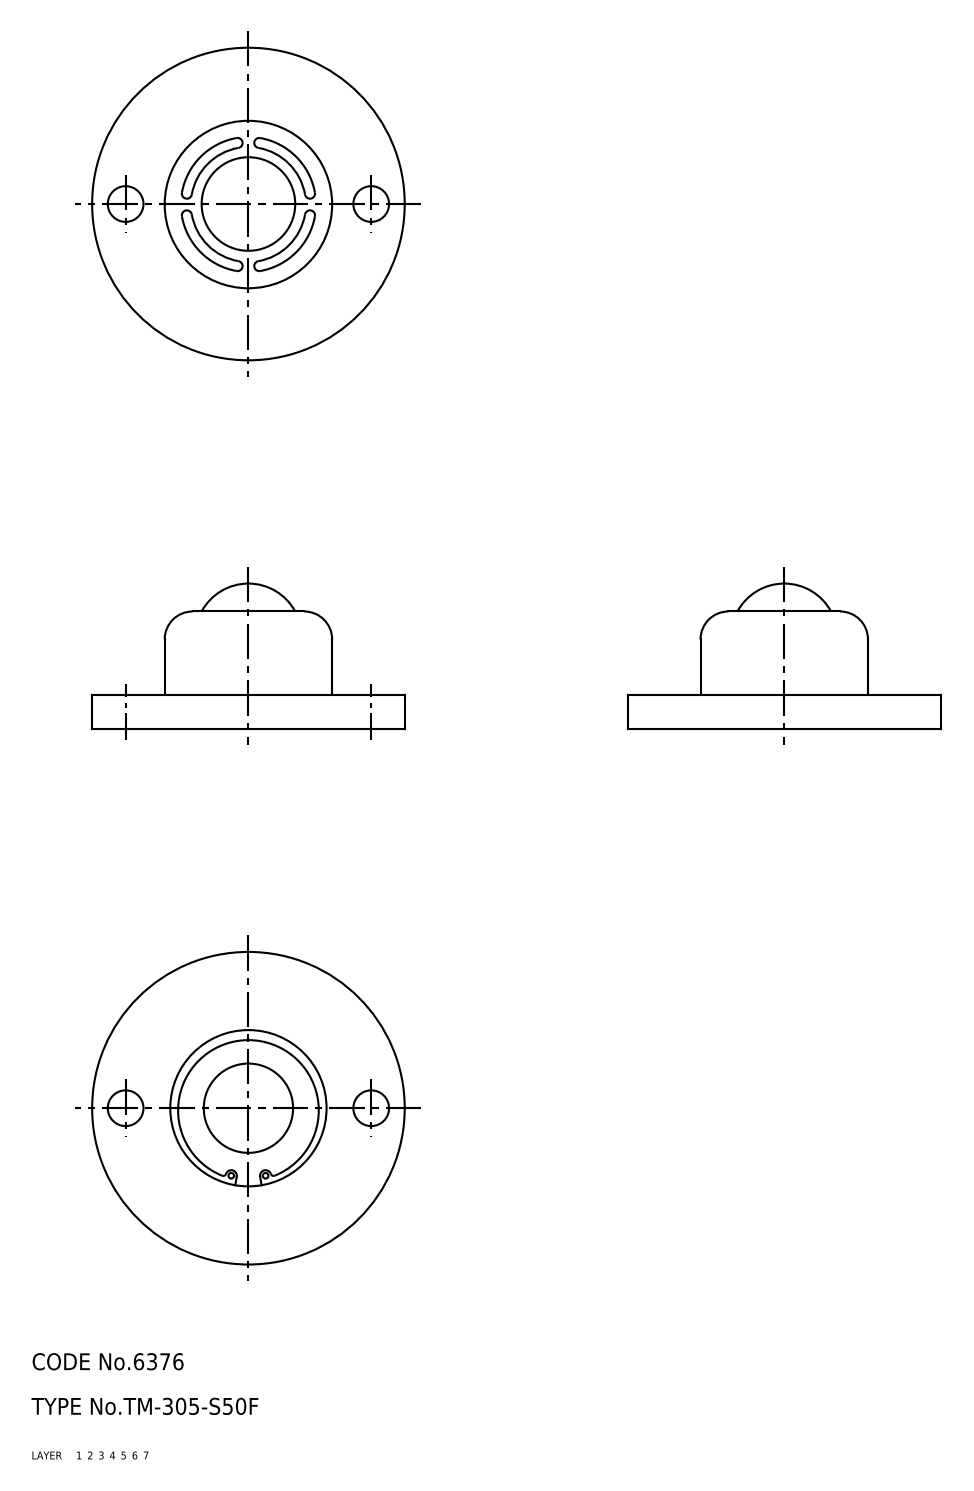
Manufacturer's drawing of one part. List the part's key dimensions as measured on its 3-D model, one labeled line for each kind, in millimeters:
Part name (STEP PRODUCT): 67113857; 67113870
STEP written by: CADfix (AUTOMOTIVE_DESIGN)
Units: millimetres
Bodies: 2 solids, 59 faces (0 planar, 0 cylindrical, 59 other)
Overall size (bounding box): 56 × 56 × 26
Volume: 18 006 mm³ · Surface area: 10 686 mm²
